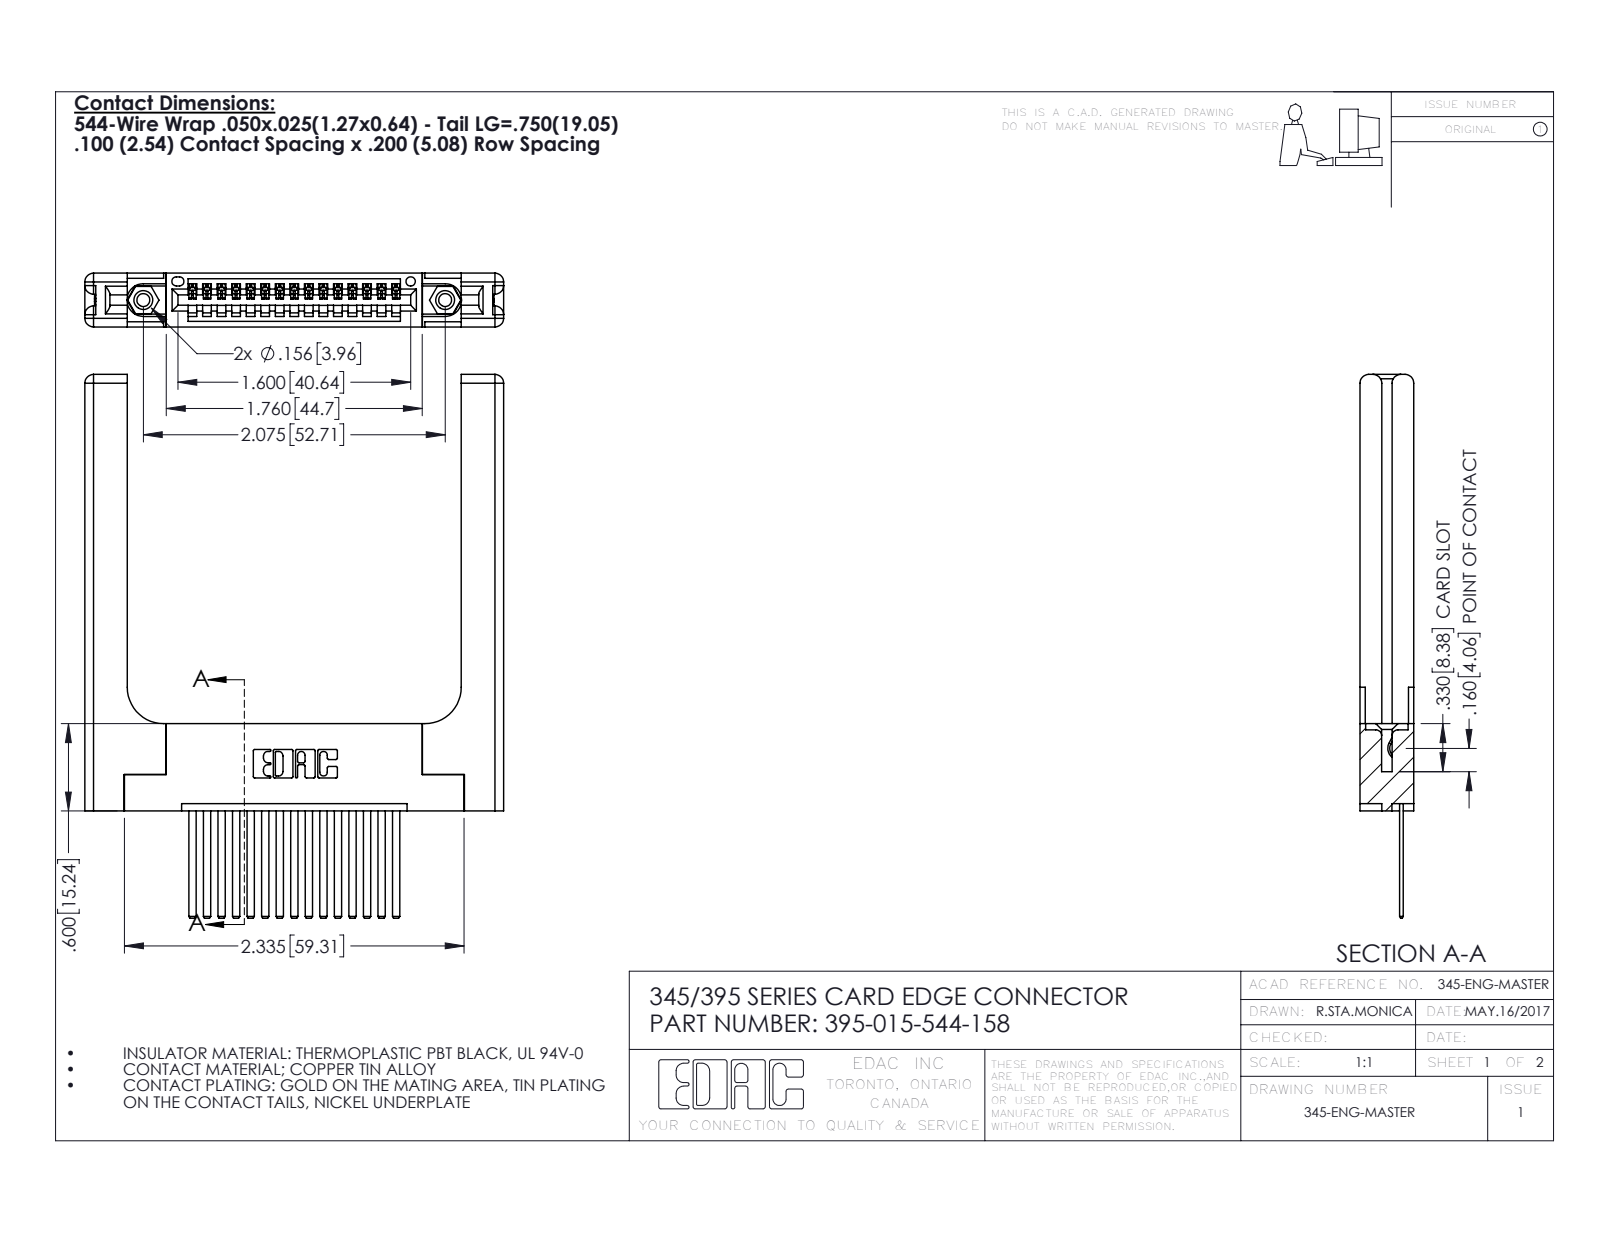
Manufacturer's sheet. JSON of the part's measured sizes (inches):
{"part_name": "345-292-001_345-293-144; 345-220-058_345-220-058; 395-015-544-158; 345-250-001_345-250-001-102 (+1 more)", "step_written_by": "SolidWorks 2016 (CONFIG_CONTROL_DESIGN)", "units": "inches", "bodies": {"solids": 20, "faces": 1162, "planar": 768, "cylindrical": 334, "other": 60}, "overall_size": [3.737, 2.879, 0.37], "volume_in3": 0.94, "surface_area_in2": 22.67, "round_holes": [[0.089, 2], [0.125, 2], [0.156, 2], [0.064, 1]], "round_bosses_or_shafts": [[0.155, 2]], "partial_cylinders_radius": [[0.006, 30], [0.01, 22], [0.06, 16], [0.007, 6], [0.031, 6], [0.026, 3], [0.03, 2], [0.031, 2]], "face_to_face_distances": [0.37, 0.072, 0.298, 0.15, 0.098, 0.272, 0.025, 0.077, 0.148, 0.2], "hole_center_spacings": [0.27, 1.842, 2.075]}
